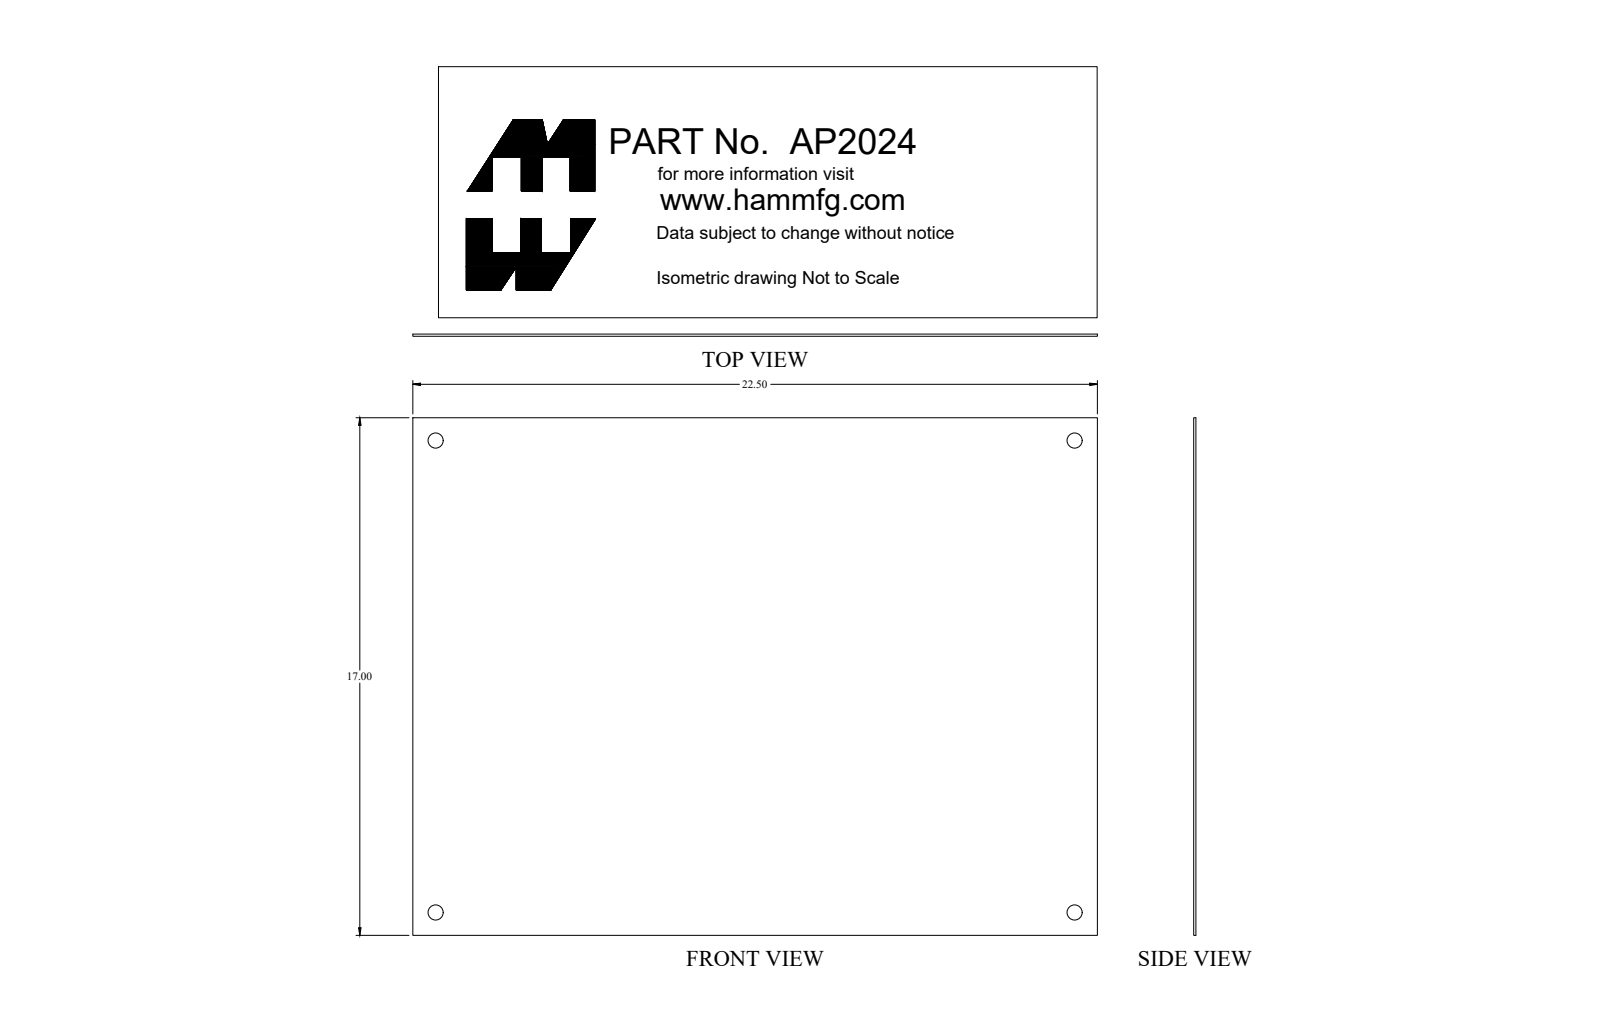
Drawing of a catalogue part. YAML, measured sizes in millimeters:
part_name: "AP2024_Default"
step_written_by: "SolidWorks 2019 (CONFIG_CONTROL_DESIGN)"
units: millimeters
bodies: {solids: 1, faces: 14, planar: 6, cylindrical: 8, other: 0}
overall_size: [571.5, 431.8, 1.8]
volume: 450300
surface_area: 496500
round_holes:
  - {diameter: 12.7, count: 4}
face_to_face_distances: [1.8, 431.8, 571.5]
hole_center_spacings: [393.7, 533.4, 663]
